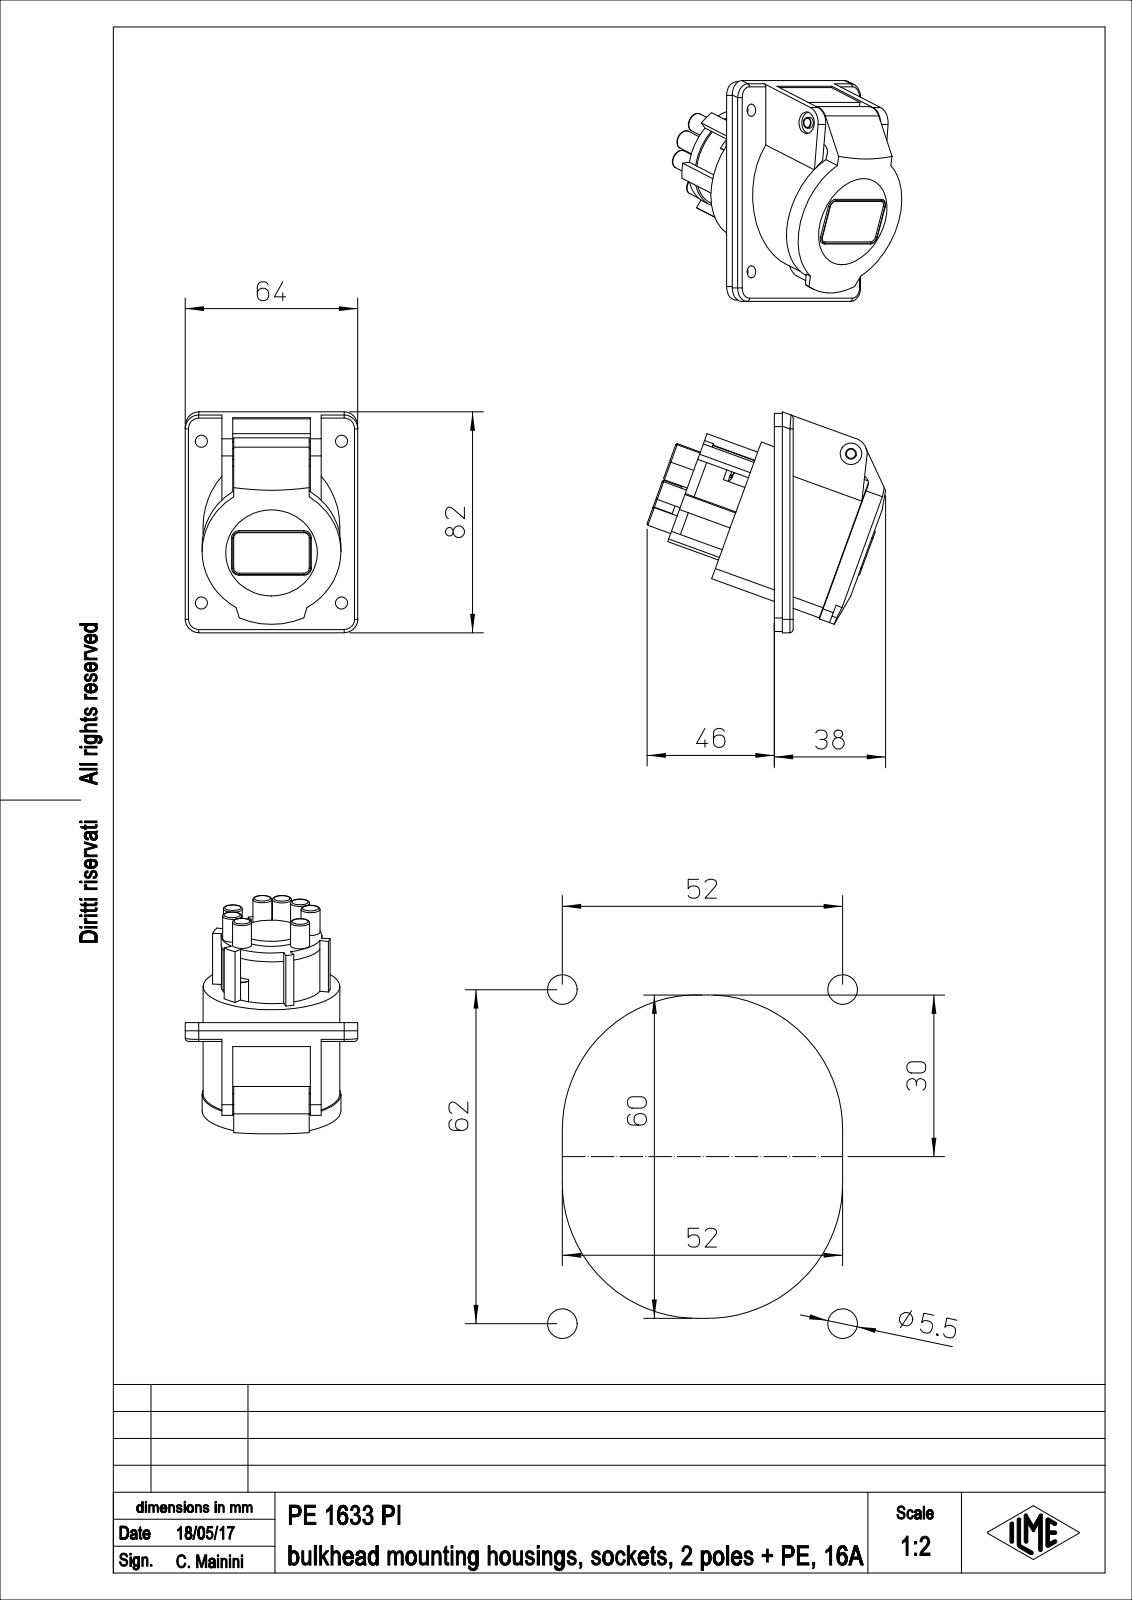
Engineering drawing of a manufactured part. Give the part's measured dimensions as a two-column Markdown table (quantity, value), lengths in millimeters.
| quantity | value |
| --- | --- |
| part name | PE_1633_PI |
| STEP written by | PTC Creo Elements/Direct Modeling 19.0E 27-Jun-2016 (C) Parametric Technology GmbH (AUTOMOTIVE_DESIGN) |
| units | millimeters |
| bodies | 1 solid, 272 faces (120 planar, 114 cylindrical, 38 other) |
| overall size | 80.6 × 77.61 × 64 |
| volume | 128 284 mm³ |
| surface area | 46 891 mm² |
| round holes (diameter × count) | 4.5 × 4, 5.5 × 4, 3.4 × 1, 8 × 1, 37.5 × 1, 44.7 × 1 |
| round bosses / shafts (diameter × count) | 7 × 8, 6.4 × 2, 50.7 × 1, 41.5 × 1, 37.4 × 1, 36 × 1, 23 × 1, 4 × 1 |
| partial cylindrical surfaces (radius × count) | 5 × 8, 0.4 × 4, 1.2 × 4, 4 × 2, 6 × 2, 6.5 × 2, 28 × 2, 2.5 × 1 |
| main face-to-face distances | 6.99, 3, 4, 1.7, 41, 8, 32.8, 42.7, 13.6, 46.4 |
| hole center spacings | 52, 79.4, 60, 60.01 |
